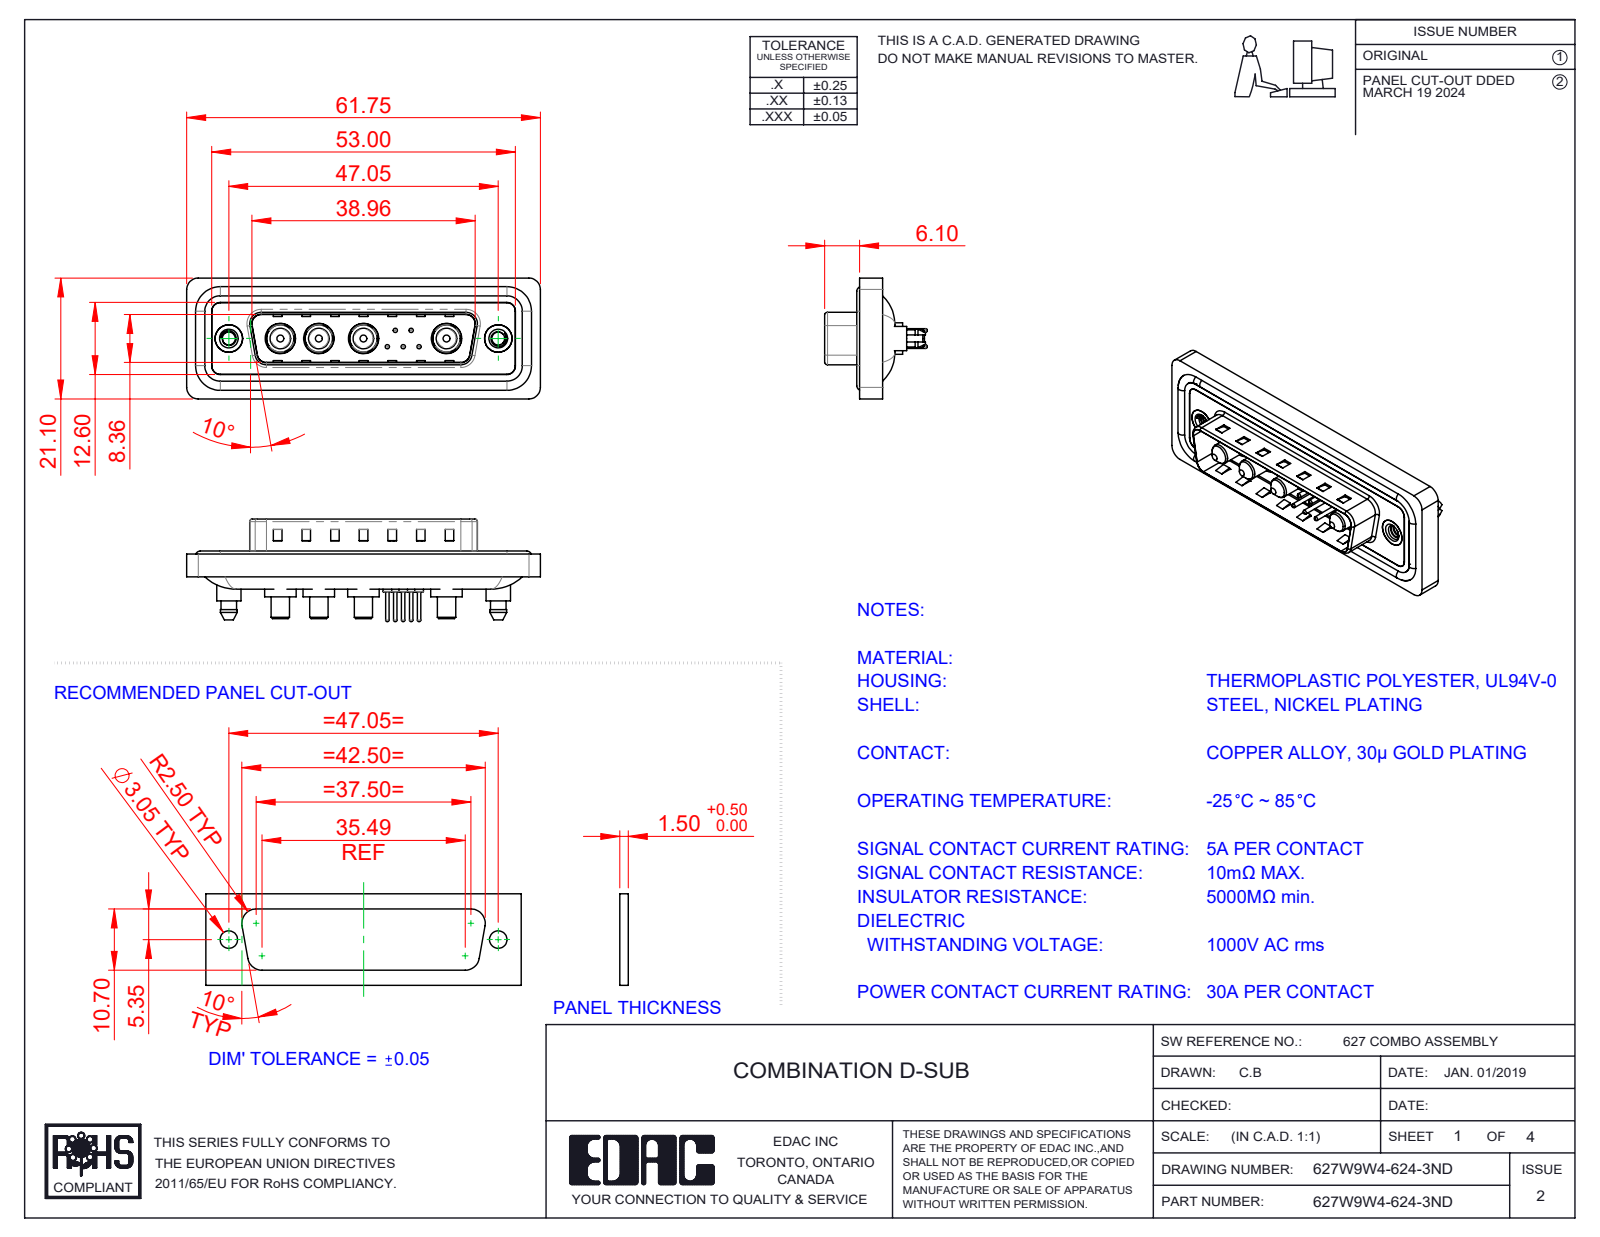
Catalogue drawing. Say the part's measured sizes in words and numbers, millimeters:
The part is named "627Combo Shell Front_25 Contacts; 627Combo Threaded Boardlock_D; 627W9W4-624-3ND; 627Combo Shell Rear_25 Contacts (+6 more)". Its 3-D file was written by "SolidWorks 2023 (CONFIG_CONTROL_DESIGN)". It is 20 solids with 882 faces: 300 planar, 374 cylindrical and 208 other. Overall it measures 61.75 by 21.1 by 17.9 millimeters. Its volume is 7 567 cubic millimeters and its surface area 12 190 square millimeters. Round holes: 5 of diameter 0.75, 5 of diameter 1.6, 5 of diameter 2, 4 of diameter 4.85, 4 of diameter 5.3, 2 of diameter 2.26, 2 of diameter 4, 2 of diameter 4.8, 2 of diameter 5. Round bosses or shafts: 5 of diameter 1.5, 5 of diameter 0.6, 4 of diameter 5.5, 4 of diameter 5.2, 4 of diameter 4.75, 4 of diameter 3.75, 4 of diameter 3.6, 4 of diameter 3.2. Partial cylindrical surfaces (rounded edges, fillets, slot ends): 24 of radius 1.5, 18 of radius 2, 10 of radius 1.6, 8 of radius 0.5, 4 of radius 0.25, 4 of radius 0.6, 4 of radius 0.65, 4 of radius 0.9. The main face-to-face distances are 0.4, 1.5, 1.1, 0.5, 3.1, 1.6, 2.9, 0.82, 9.58, 5.65. The hole center spacings are 3.16, 2.77, 5.04, 14.51, 2.78, 4.4, 4.41, 5.
